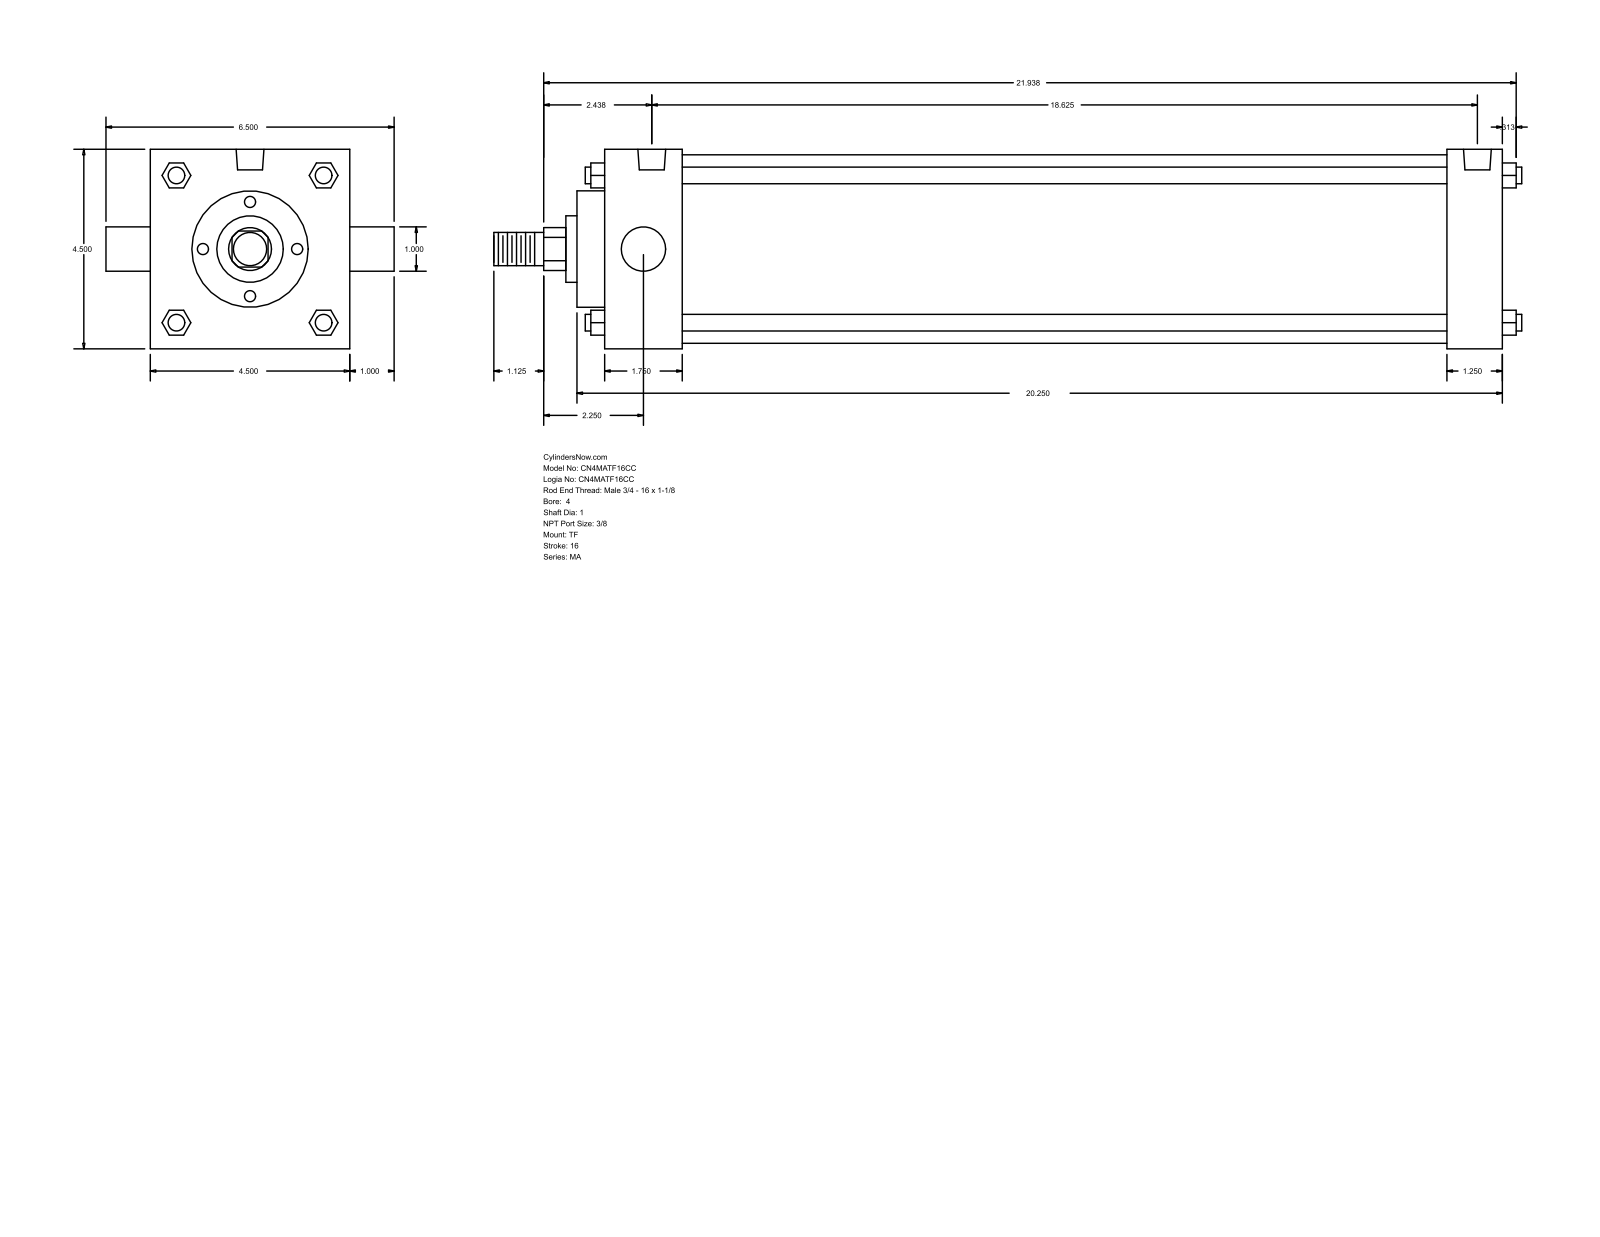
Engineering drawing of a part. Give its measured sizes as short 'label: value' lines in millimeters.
name: MA_TF__0400_1
written by: GSSL Pune (CONFIG_CONTROL_DESIGN)
unit: mm
bodies: 0 solids, 122 faces (93 planar, 29 cylindrical, 0 other)
size: 588.96 × 165.1 × 114.3
holes: 3× ⌀11.11, 2× ⌀15.93
bosses: 4× ⌀9.53, 2× ⌀25.4, 1× ⌀107.95, 1× ⌀66.67, 1× ⌀38.1, 1× ⌀19.05
rounds: 1× R12.29
face distances: 114.3, 514.35, 482.6, 31.75, 44.46, 438.14, 469.89, 530.22, 15.87, 60.33
hole spacings: 4.76, 468.32, 463.56, 473.08
